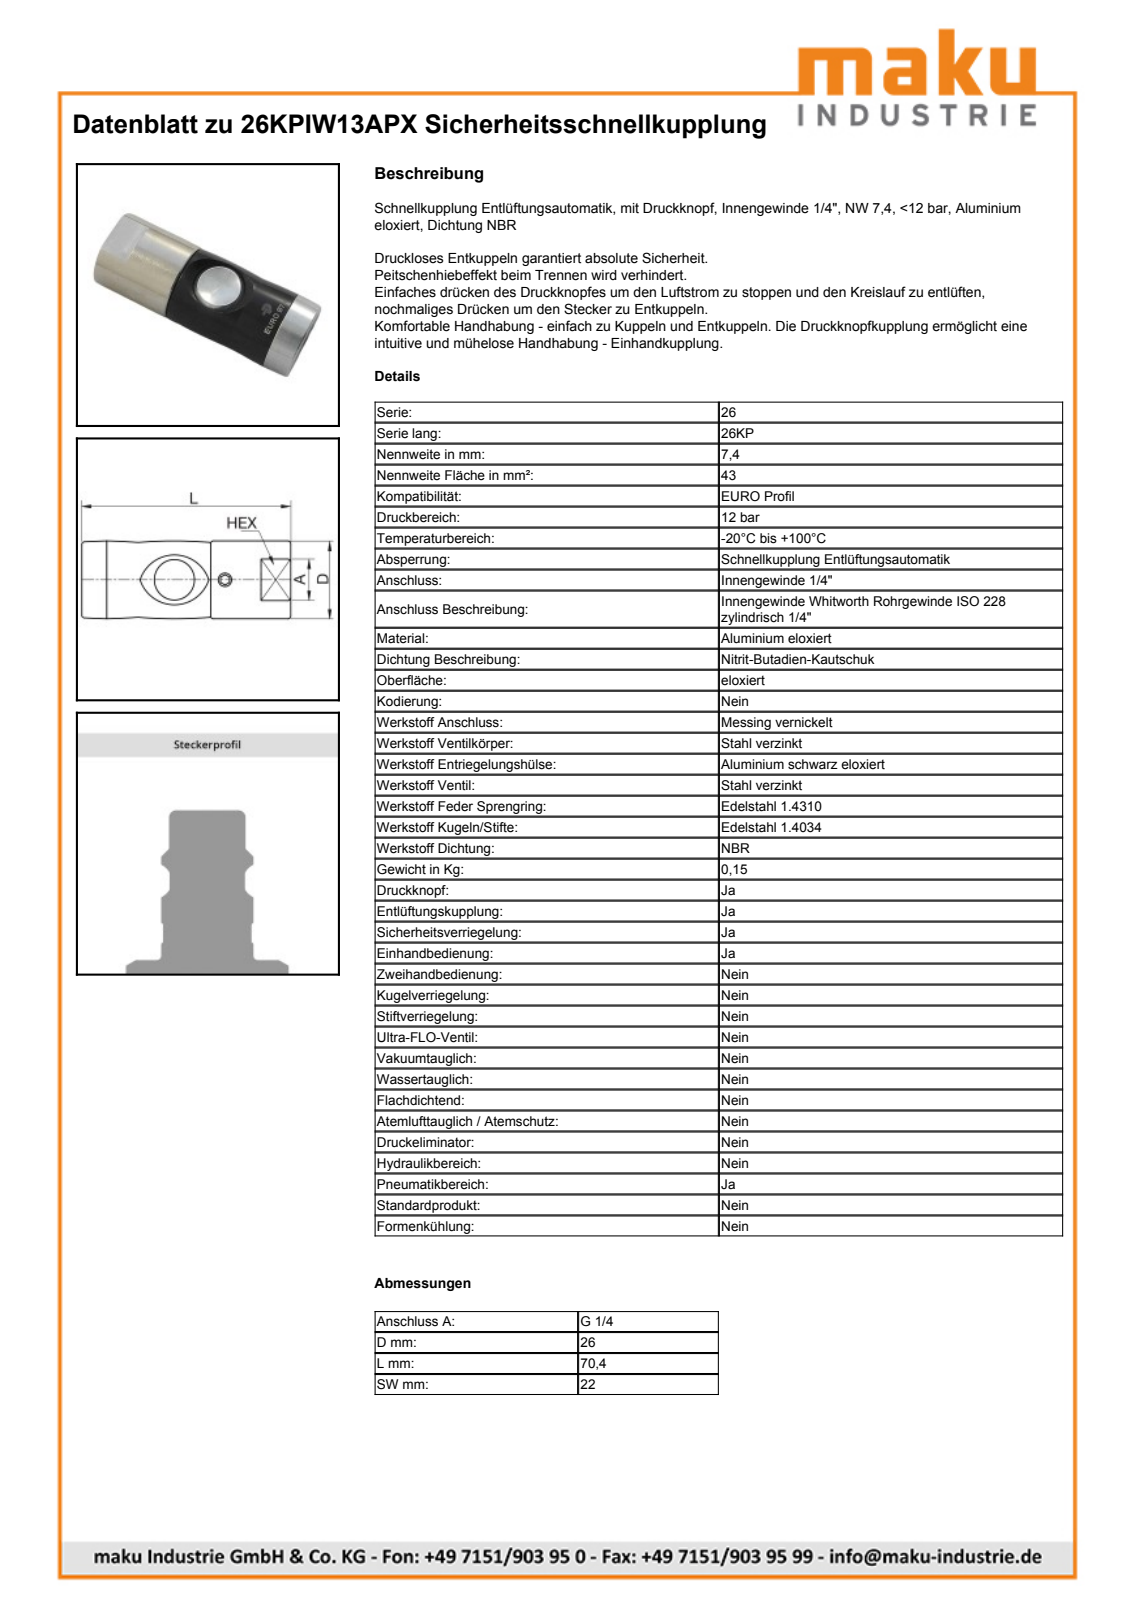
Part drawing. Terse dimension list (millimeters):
name: 26KPIW13APX
written by: Autodesk Inventor 2019 (AUTOMOTIVE_DESIGN)
unit: mm
bodies: 39 solids, 256 faces (71 planar, 87 cylindrical, 98 other)
size: 70.4 × 26 × 26
volume: 38 709 mm³; area: 24 408 mm²
holes: 2× ⌀12.4, 1× ⌀3.5, 1× ⌀6.5, 1× ⌀7, 1× ⌀9.65, 1× ⌀10.1, 1× ⌀10.6, 1× ⌀11.45, 1× ⌀12.1, 1× ⌀12.25, 1× ⌀12.8, 1× ⌀13.6
bosses: 1× ⌀26, 1× ⌀22, 1× ⌀21.31, 1× ⌀18.1, 1× ⌀17.8, 1× ⌀16.5, 1× ⌀15.8, 1× ⌀15.38
rounds: 2× R6.2, 1× R4.4
face distances: 43.4, 8.4, 35, 27, 62, 70.4, 12.06, 14.94, 49.94, 58.34
hole spacings: 0.6, 0.7, 1.3, 17.05
